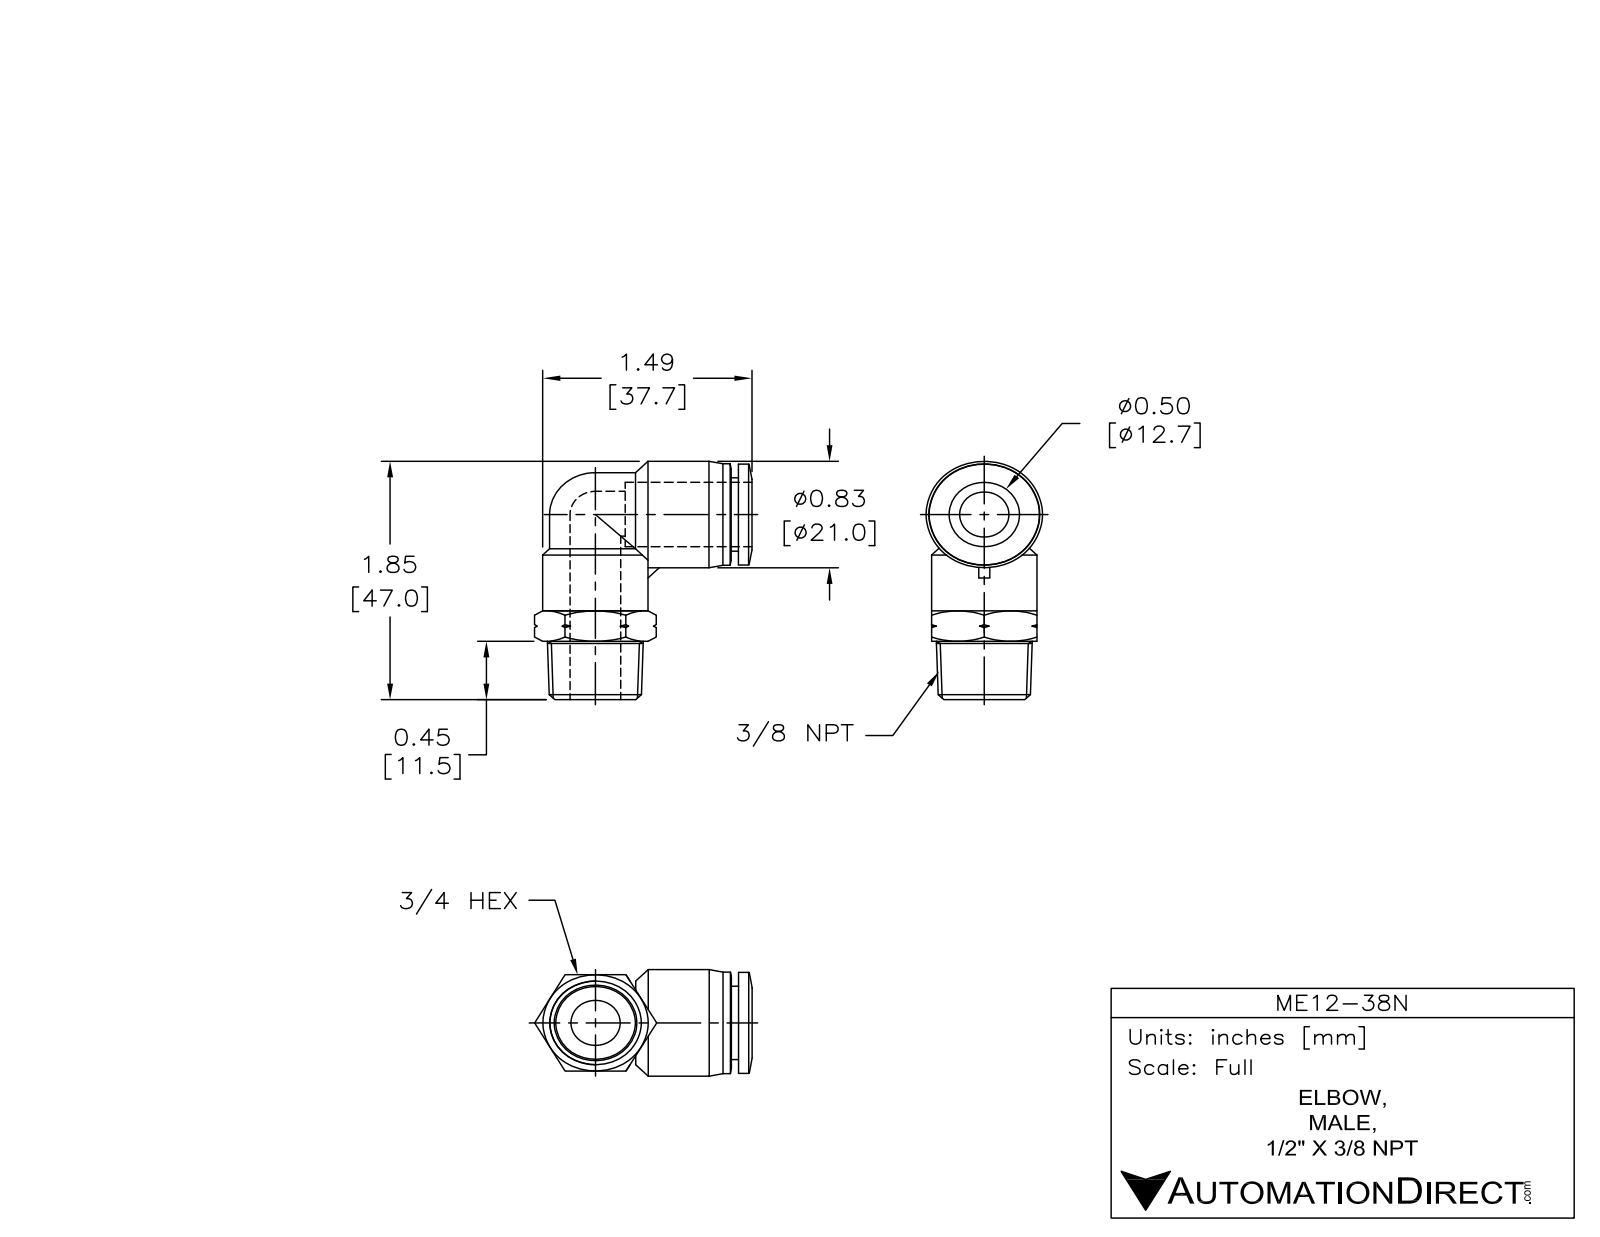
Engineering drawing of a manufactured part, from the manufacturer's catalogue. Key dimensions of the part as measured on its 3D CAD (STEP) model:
Part name (STEP PRODUCT): ME12-38N
STEP written by: SolidWorks 2015 (AUTOMOTIVE_DESIGN)
Units: inches
Bodies: 1 solid, 85 faces (14 planar, 20 cylindrical, 51 other)
Overall size (bounding box): 1.85 × 1.544 × 0.827
Volume: 0.712 in³ · Surface area: 10.18 in²
Round holes (diameter × count): ⌀0.354 ×2, ⌀0.51 ×1
Round bosses / shafts (diameter × count): ⌀0.65 ×2, ⌀0.827 ×1, ⌀0.787 ×1, ⌀0.783 ×1, ⌀0.748 ×1, ⌀0.569 ×1
Main face-to-face distances: 0.748, 0.051, 0.762, 0.813, 0.453, 0.335, 0.413, 0.079
